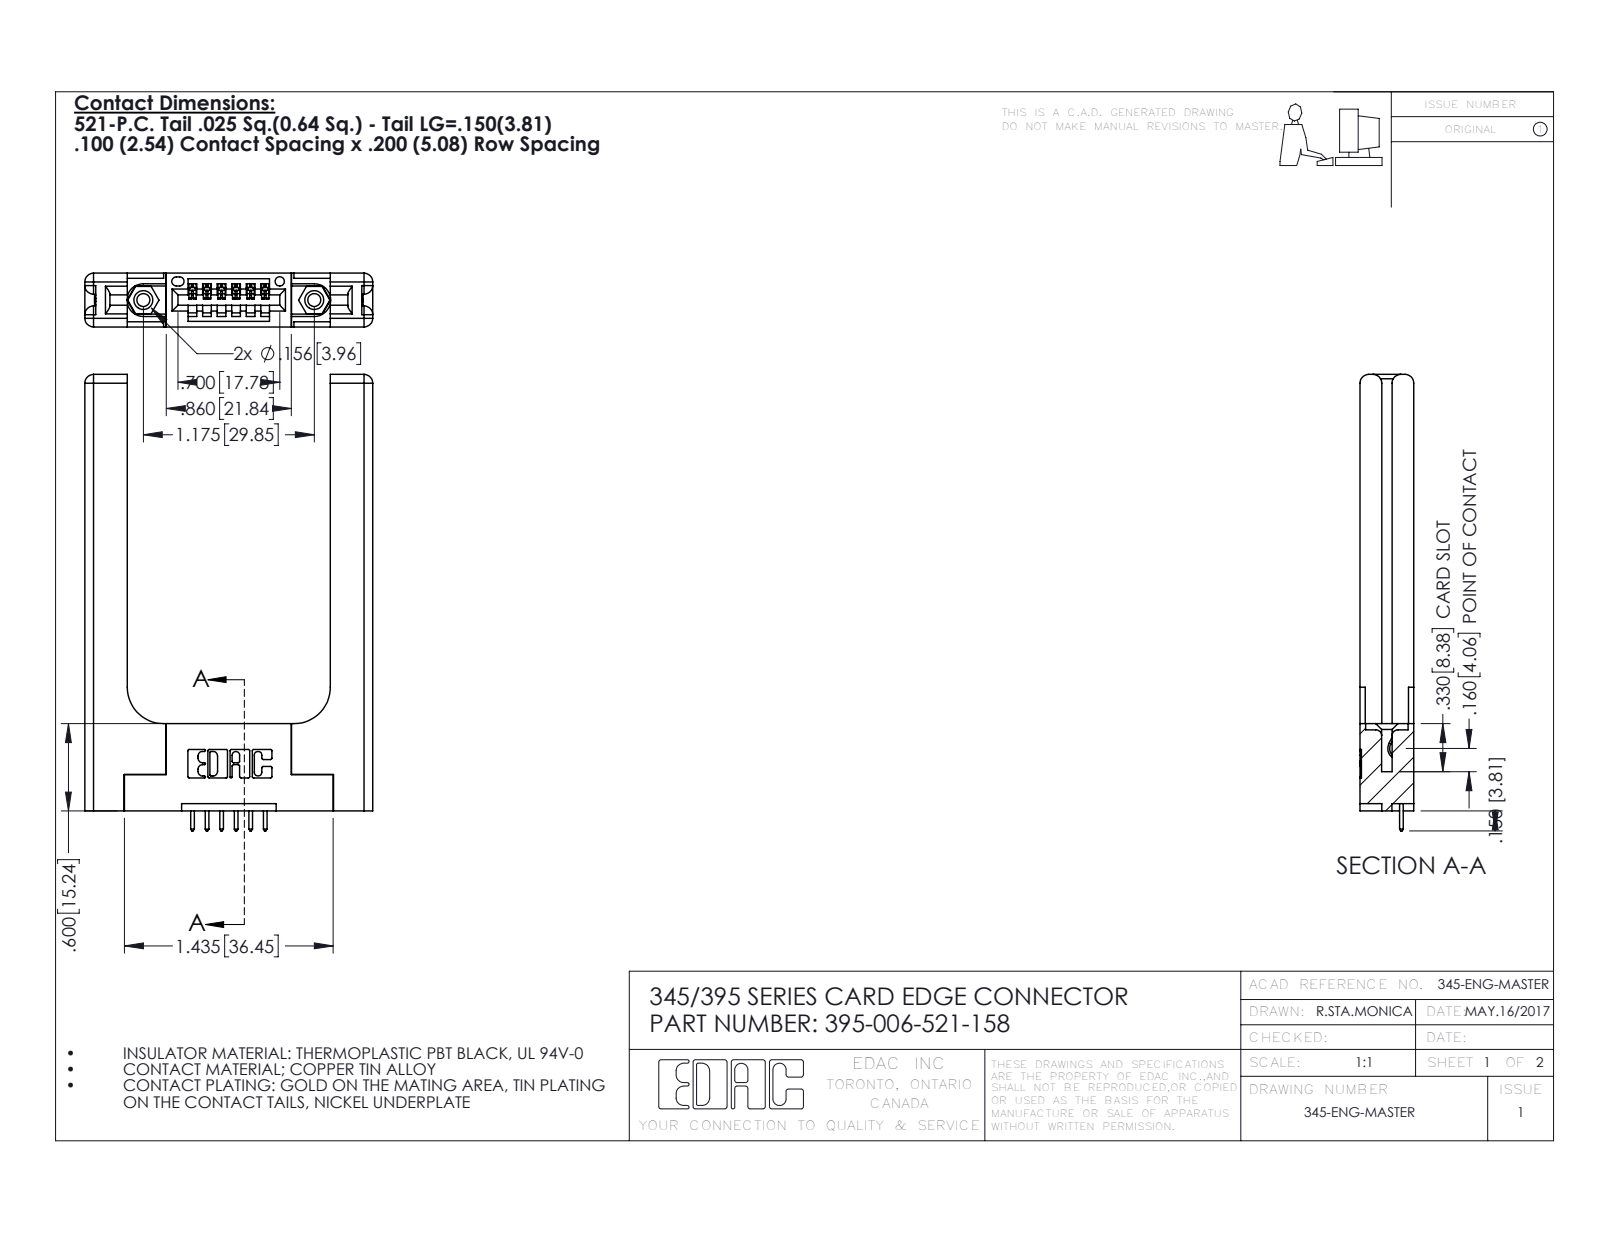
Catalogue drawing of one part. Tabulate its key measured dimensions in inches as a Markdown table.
| quantity | value |
| --- | --- |
| part name | 345-220-058_345-220-058; 345-292-001_345-293-121; 345-250-001_345-250-001-102; 395-006-521-158 (+1 more) |
| STEP written by | SolidWorks 2016 (CONFIG_CONTROL_DESIGN) |
| units | inches |
| bodies | 11 solids, 730 faces (468 planar, 202 cylindrical, 60 other) |
| overall size | 3.137 × 1.979 × 0.37 |
| volume | 0.791 in³ |
| surface area | 16.55 in² |
| round holes (diameter × count) | 0.089 × 2, 0.125 × 2, 0.156 × 2, 0.064 × 1 |
| round bosses / shafts (diameter × count) | 0.155 × 2 |
| partial cylindrical surfaces (radius × count) | 0.01 × 22, 0.06 × 16, 0.006 × 12, 0.01 × 12, 0.007 × 6, 0.031 × 6, 0.026 × 3, 0.03 × 2 |
| main face-to-face distances | 0.37, 0.15, 0.22, 0.072, 1.396, 0.077, 0.148, 0.298, 0.071, 0.292 |
| hole center spacings | 0.27, 0.946, 1.175 |
